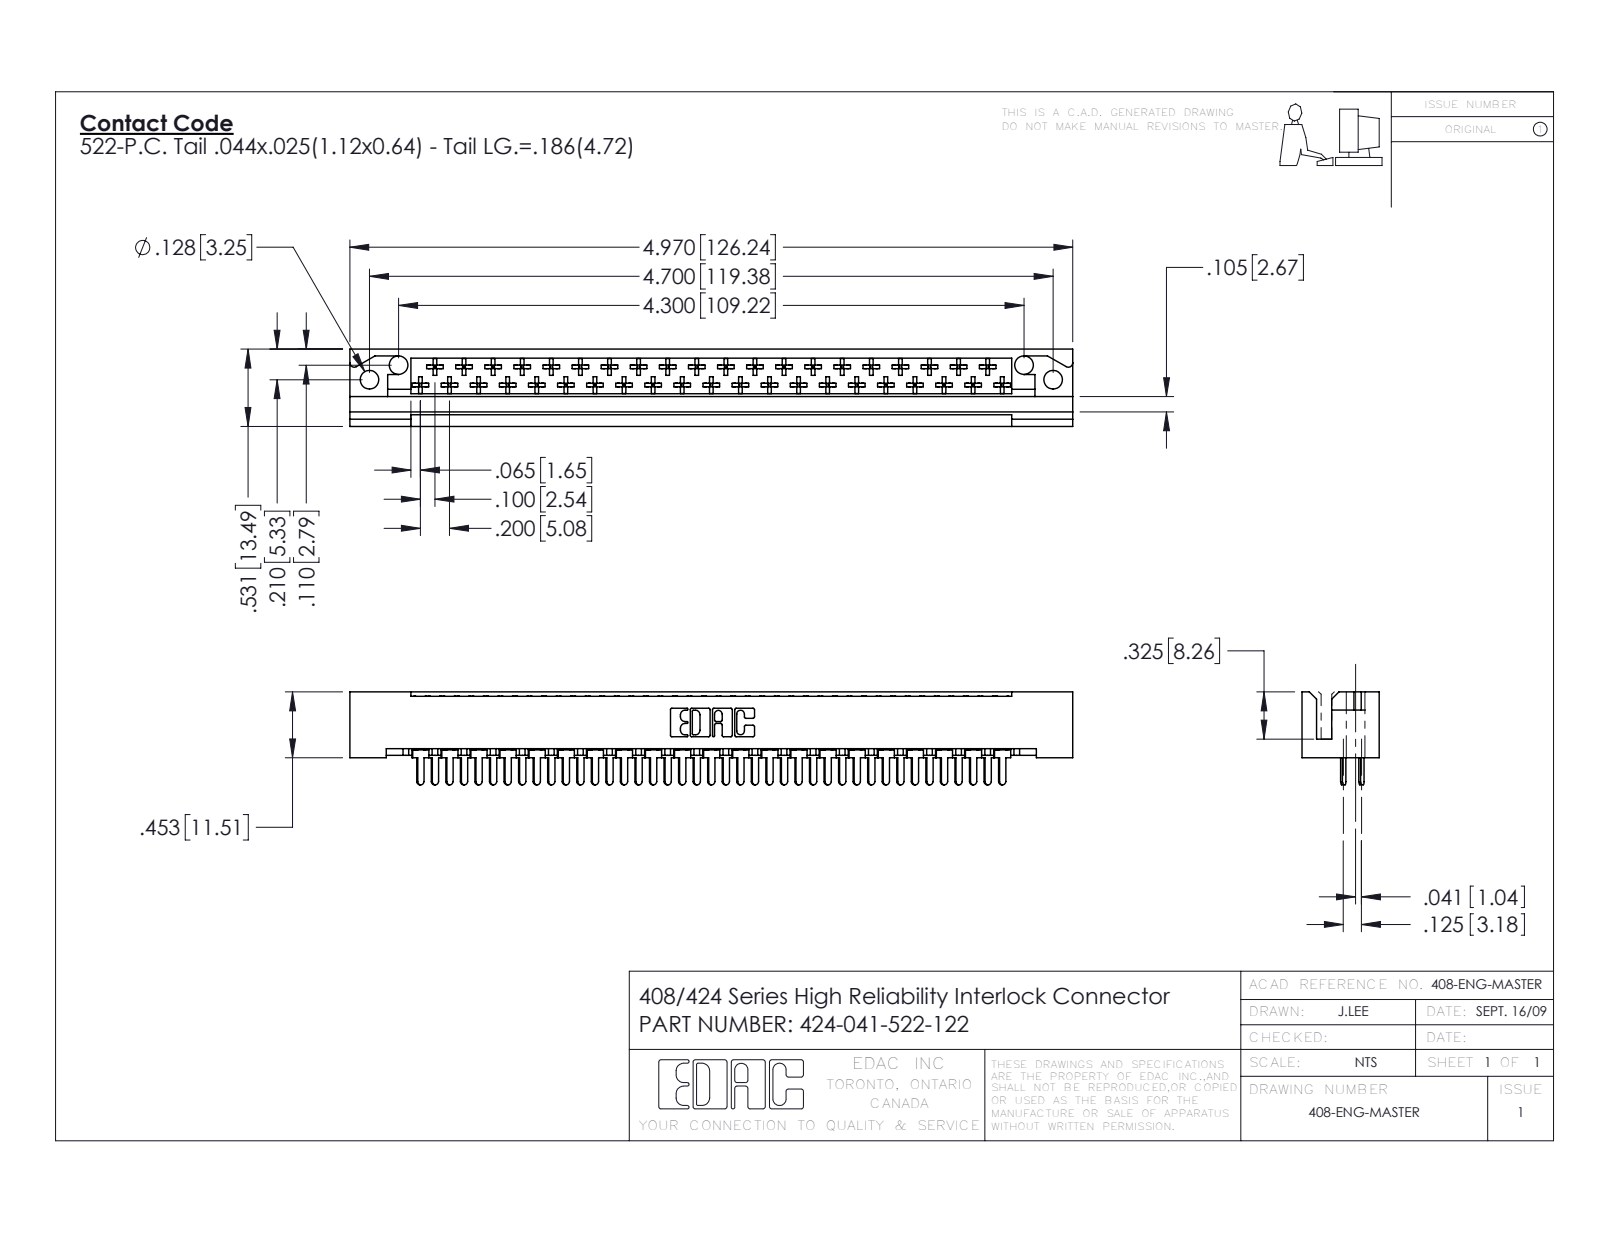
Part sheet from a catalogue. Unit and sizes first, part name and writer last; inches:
Units: inches
Overall size (bounding box): 4.97 × 0.639 × 0.531
Round holes (diameter × count): ⌀0.128 ×4
Partial cylindrical surfaces — rounded edges, fillets, slot ends (radius × count): R0.01 ×246, R0.02 ×43, R0.022 ×41, R0.01 ×22, R0.007 ×6, R0.031 ×6, R0.026 ×3, R0.03 ×2
Main face-to-face distances: 0.1, 0.296, 0.025, 0.531, 0.125, 0.272, 0.235, 0.259, 0.025, 0.217
Hole centre spacings: 0.224, 4.501, 4.3, 4.7
Volume: 0.799 in³ · Surface area: 26.83 in²
Bodies: 42 solids, 2400 faces (1811 planar, 425 cylindrical, 164 other)
Part name (STEP PRODUCT): 424-041-522-122; 408-290-001_408-290-122; 424 Part_041
STEP written by: SolidWorks 2016 (CONFIG_CONTROL_DESIGN)
